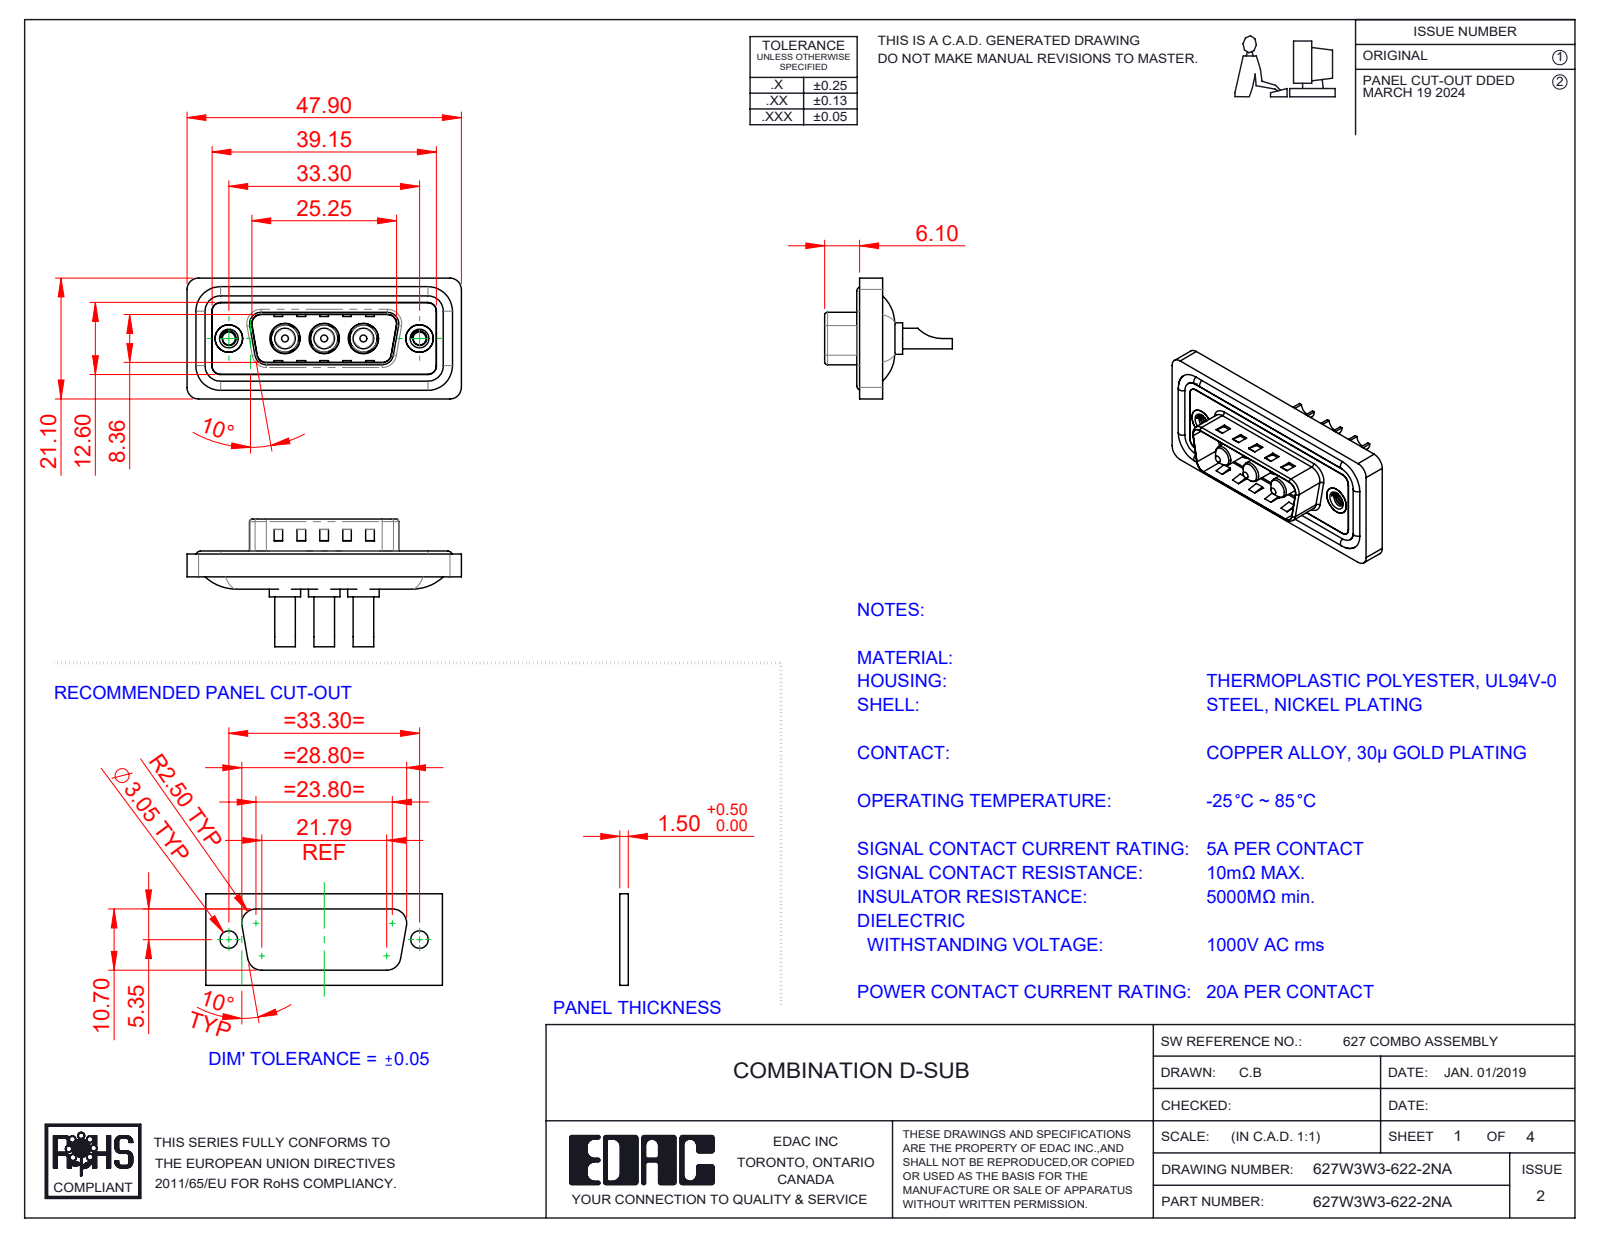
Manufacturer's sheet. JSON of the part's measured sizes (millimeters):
{"part_name": "627Combo Housing_3W3; 627Combo Shell Rear_15 Contacts; Power Pin_20A SC; 627Combo Waterproof Housing_15 Contacts (+3 more)", "step_written_by": "SolidWorks 2023 (CONFIG_CONTROL_DESIGN)", "units": "millimeters", "bodies": {"solids": 13, "faces": 583, "planar": 216, "cylindrical": 252, "other": 115}, "overall_size": [47.9, 22.3, 21.1], "volume_mm3": 5626, "surface_area_mm2": 8998, "round_holes": [[2.7, 3], [4.85, 3], [5.3, 3], [2.26, 2], [4, 2], [4.8, 2], [5, 2]], "round_bosses_or_shafts": [[1.6, 4], [5.5, 3], [5.2, 3], [4.75, 3], [3.75, 3], [3.6, 3], [4.9, 2]], "partial_cylinders_radius": [[1.5, 26], [2, 20], [0.5, 8], [1.6, 8], [0.25, 4], [0.6, 4], [0.65, 4], [0.9, 4]], "face_to_face_distances": [0.4, 1.1, 1.5, 0.5, 1.6, 3.1, 2.9, 4, 0.82, 9.58], "hole_center_spacings": [6.85, 9.8, 16.65, 23.5, 13.7, 33.3]}
